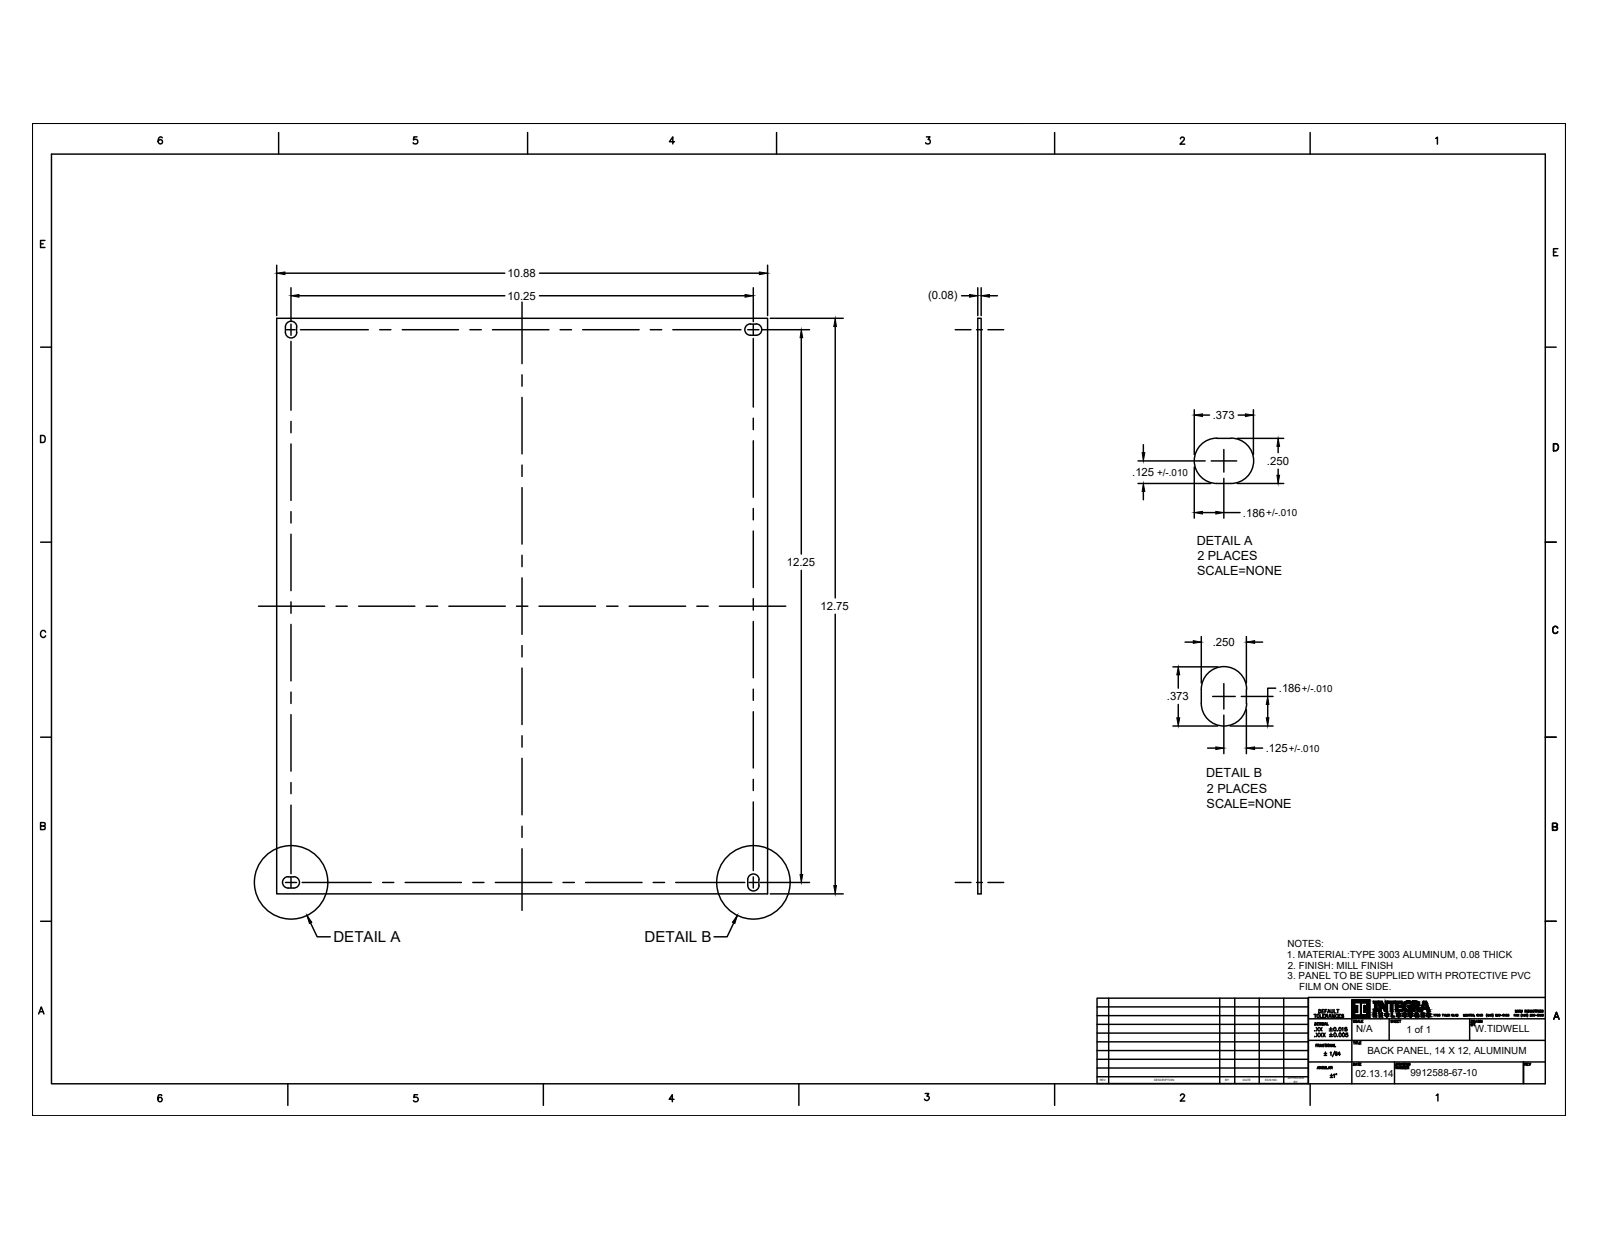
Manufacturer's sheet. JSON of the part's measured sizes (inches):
{"part_name": "9912588-67-10", "step_written_by": "CREO PARAMETRIC BY PTC INC, 2018050 (CONFIG_CONTROL_DESIGN)", "units": "inches", "bodies": {"solids": 1, "faces": 22, "planar": 14, "cylindrical": 8, "other": 0}, "overall_size": [12.75, 10.88, 0.08], "volume_in3": 11.07, "surface_area_in2": 280.9, "partial_cylinders_radius": [[0.125, 8]], "face_to_face_distances": [0.08, 10.88, 12.75, 0.25, 0.125, 0.375, 12.375, 12.625, 12.25, 0.19]}
